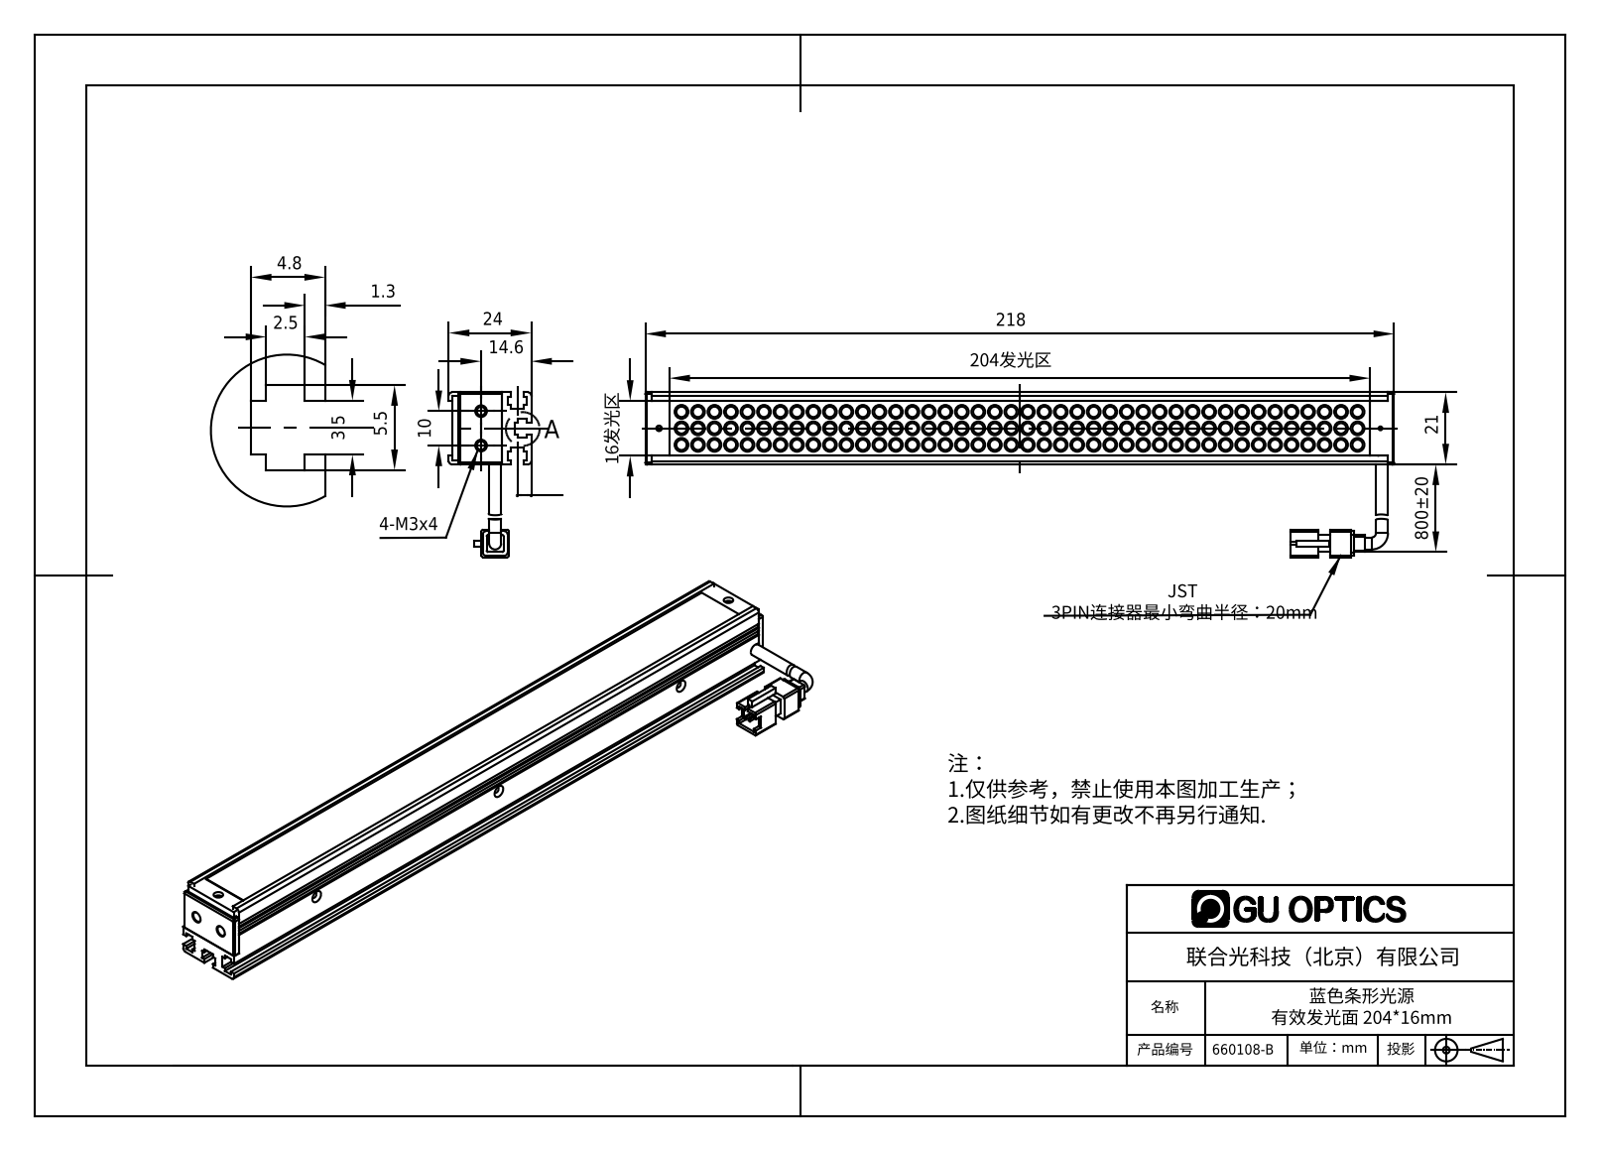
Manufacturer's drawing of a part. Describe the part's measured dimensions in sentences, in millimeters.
The part is named "660108-B". Its 3-D file was written by "SolidWorks 2016 (AUTOMOTIVE_DESIGN)". It is 8 solids with 1201 faces: 377 planar, 591 cylindrical and 233 other. Overall it measures 218 by 48 by 24 millimeters. Its volume is 62 599 cubic millimeters and its surface area 69 705 square millimeters. Round holes: 5 of diameter 1.6, 3 of diameter 1.7, 2 of diameter 1.5, 2 of diameter 2.5, 2 of diameter 2.8, 2 of diameter 3, 1 of diameter 1.1, 1 of diameter 1.25, 1 of diameter 2. Round bosses or shafts: 126 of diameter 4, 126 of diameter 3, 2 of diameter 3.5. Partial cylindrical surfaces (rounded edges, fillets, slot ends): 12 of radius 1, 8 of radius 0.5, 1 of radius 1.65. The main face-to-face distances are 1, 2.5, 2, 18.5, 21, 4, 3.5, 2.3, 21.1, 23.1. The hole center spacings are 210, 7, 30.04, 30.48, 75, 105.01, 105.14, 180.01.
